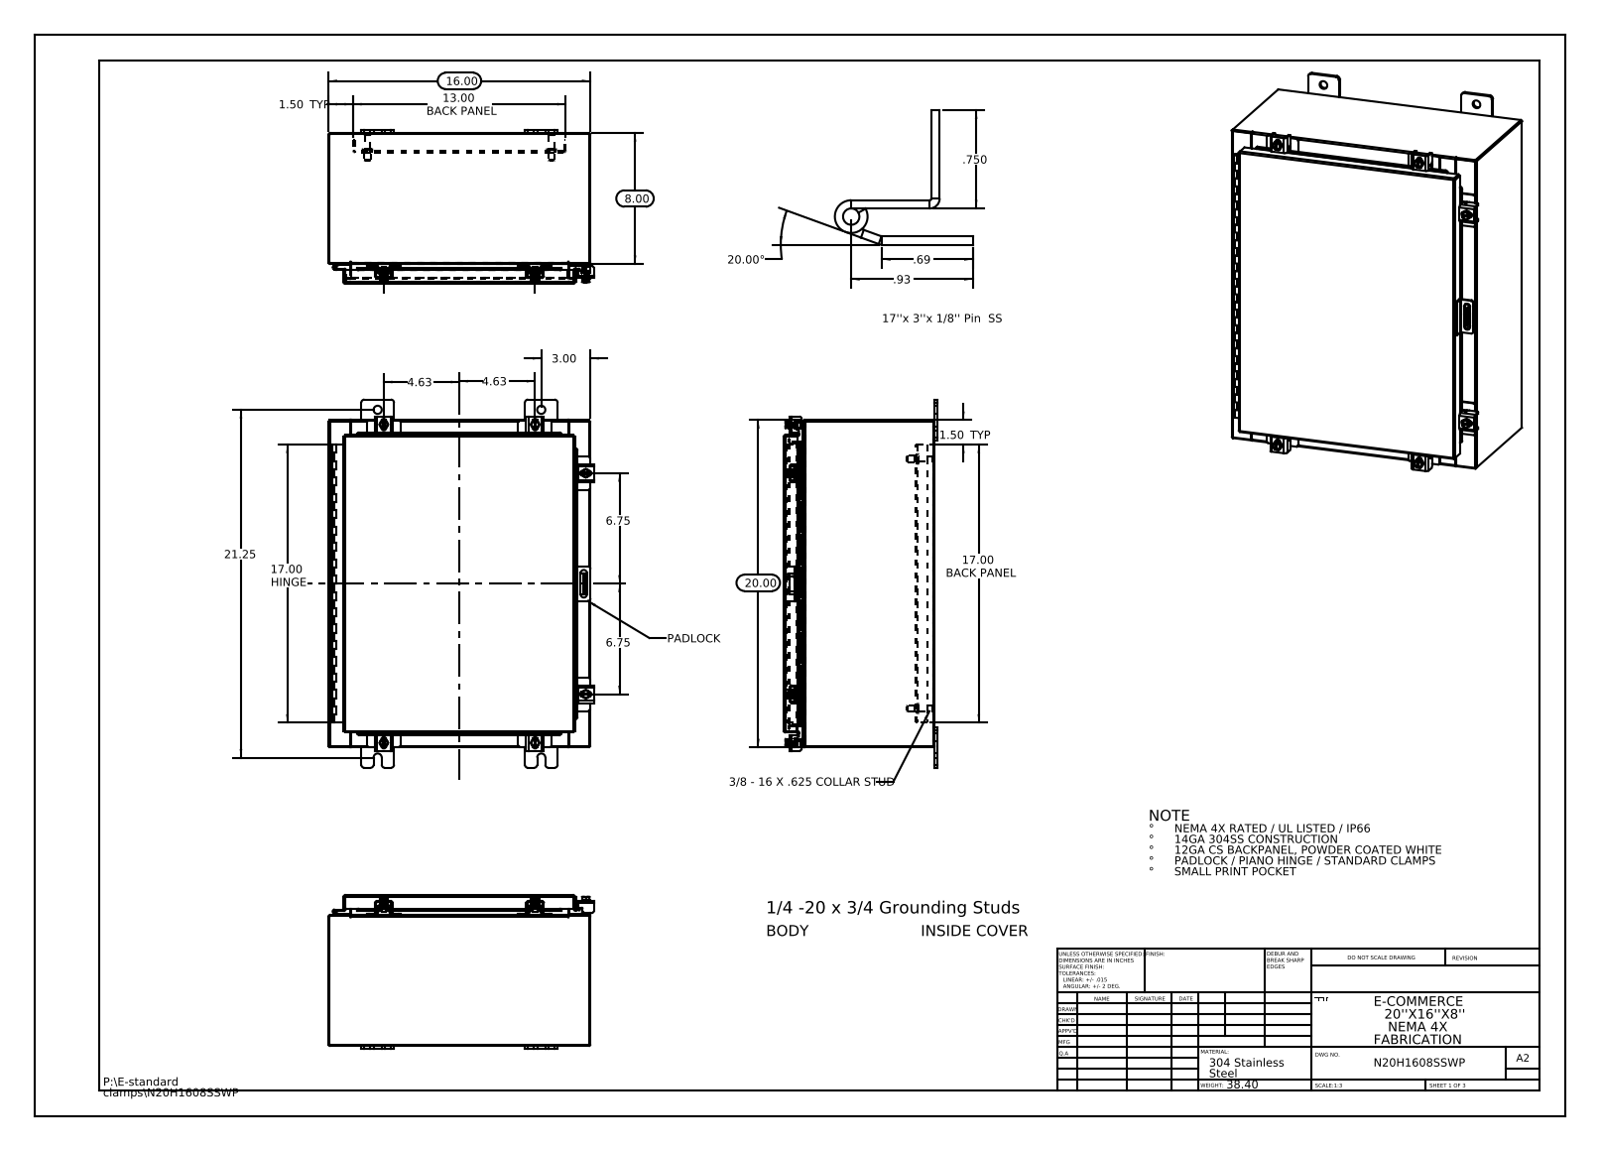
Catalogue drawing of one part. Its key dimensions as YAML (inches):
part_name: "N20H1608SSWP 125 Pin Hinge; N20H1608SSWP Hinge Cover Side; N20H1608SSWP 22104005_DEFAULT; N20H1608SSWP 22101002 (+8 more)"
step_written_by: "SolidWorks 2013 (CONFIG_CONTROL_DESIGN)"
units: inches
bodies: {solids: 47, faces: 1613, planar: 860, cylindrical: 657, other: 96}
overall_size: [22.5, 16.211, 9.389]
volume: 135.6
surface_area: 3435
round_holes:
  - {diameter: 0.5, count: 8}
  - {diameter: 0.213, count: 6}
  - {diameter: 0.26, count: 6}
  - {diameter: 0.125, count: 2}
  - {diameter: 0.125, count: 1}
round_bosses_or_shafts:
  - {diameter: 0.25, count: 7}
  - {diameter: 0.5, count: 6}
  - {diameter: 0.399, count: 6}
  - {diameter: 0.625, count: 4}
  - {diameter: 0.375, count: 4}
  - {diameter: 0.33, count: 4}
partial_cylinders:
  - {radius: 0.06, count: 30}
  - {radius: 0.013, count: 25}
  - {radius: 0.19, count: 24}
  - {radius: 0.088, count: 21}
  - {radius: 0.12, count: 12}
  - {radius: 0.141, count: 12}
  - {radius: 0.125, count: 10}
  - {radius: 0.05, count: 9}
face_to_face_distances: [0.075, 9.126, 15.925, 9.201, 9.051, 19.925, 0.104, 1, 1.075, 8.051]
hole_center_spacings: [17.38, 1.858, 2.276, 2.326, 2.326, 3.065, 4.297, 9.25]
